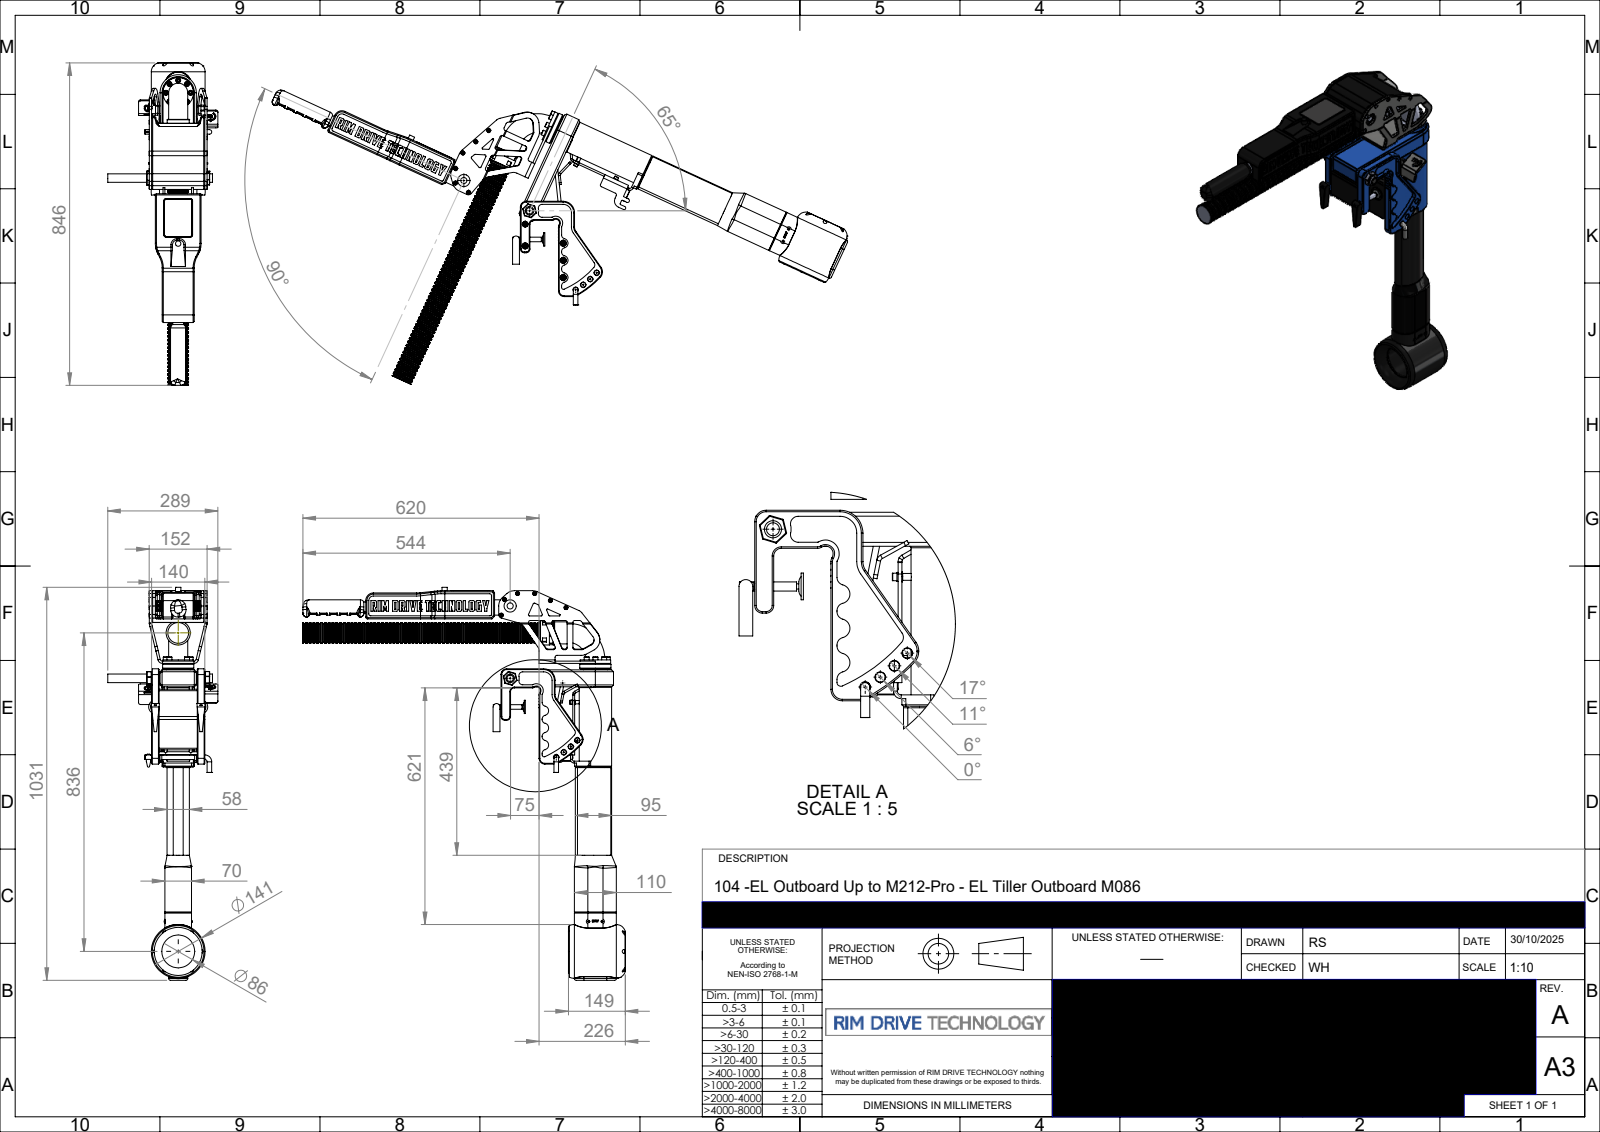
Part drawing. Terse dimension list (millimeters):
name: P-104-250-rev-A-086
written by: SolidWorks 2024 (AUTOMOTIVE_DESIGN)
unit: mm
bodies: 1 solid, 3457 faces (1622 planar, 748 cylindrical, 1087 other)
size: 1031.47 × 846.29 × 288.95
volume: 12 800 000 mm³; area: 1 258 000 mm²
holes: 5× ⌀5, 4× ⌀13, 2× ⌀4.3, 1× ⌀4, 1× ⌀17, 1× ⌀32, 1× ⌀85, 1× ⌀86.5, 1× ⌀90.5
bosses: 8× ⌀13, 7× ⌀12, 6× ⌀9.64, 4× ⌀10, 3× ⌀8.1, 2× ⌀35, 2× ⌀7.64, 2× ⌀6.95
rounds: 60× R3, 49× R5, 47× R0.5, 34× R10, 26× R2, 25× R1, 12× R6, 7× R15
face distances: 6, 20, 10, 5, 120, 110, 15, 100, 95, 12.5
hole spacings: 239.77, 23.7, 36.5, 47.35, 61.28, 644.27, 23.71, 42.5
